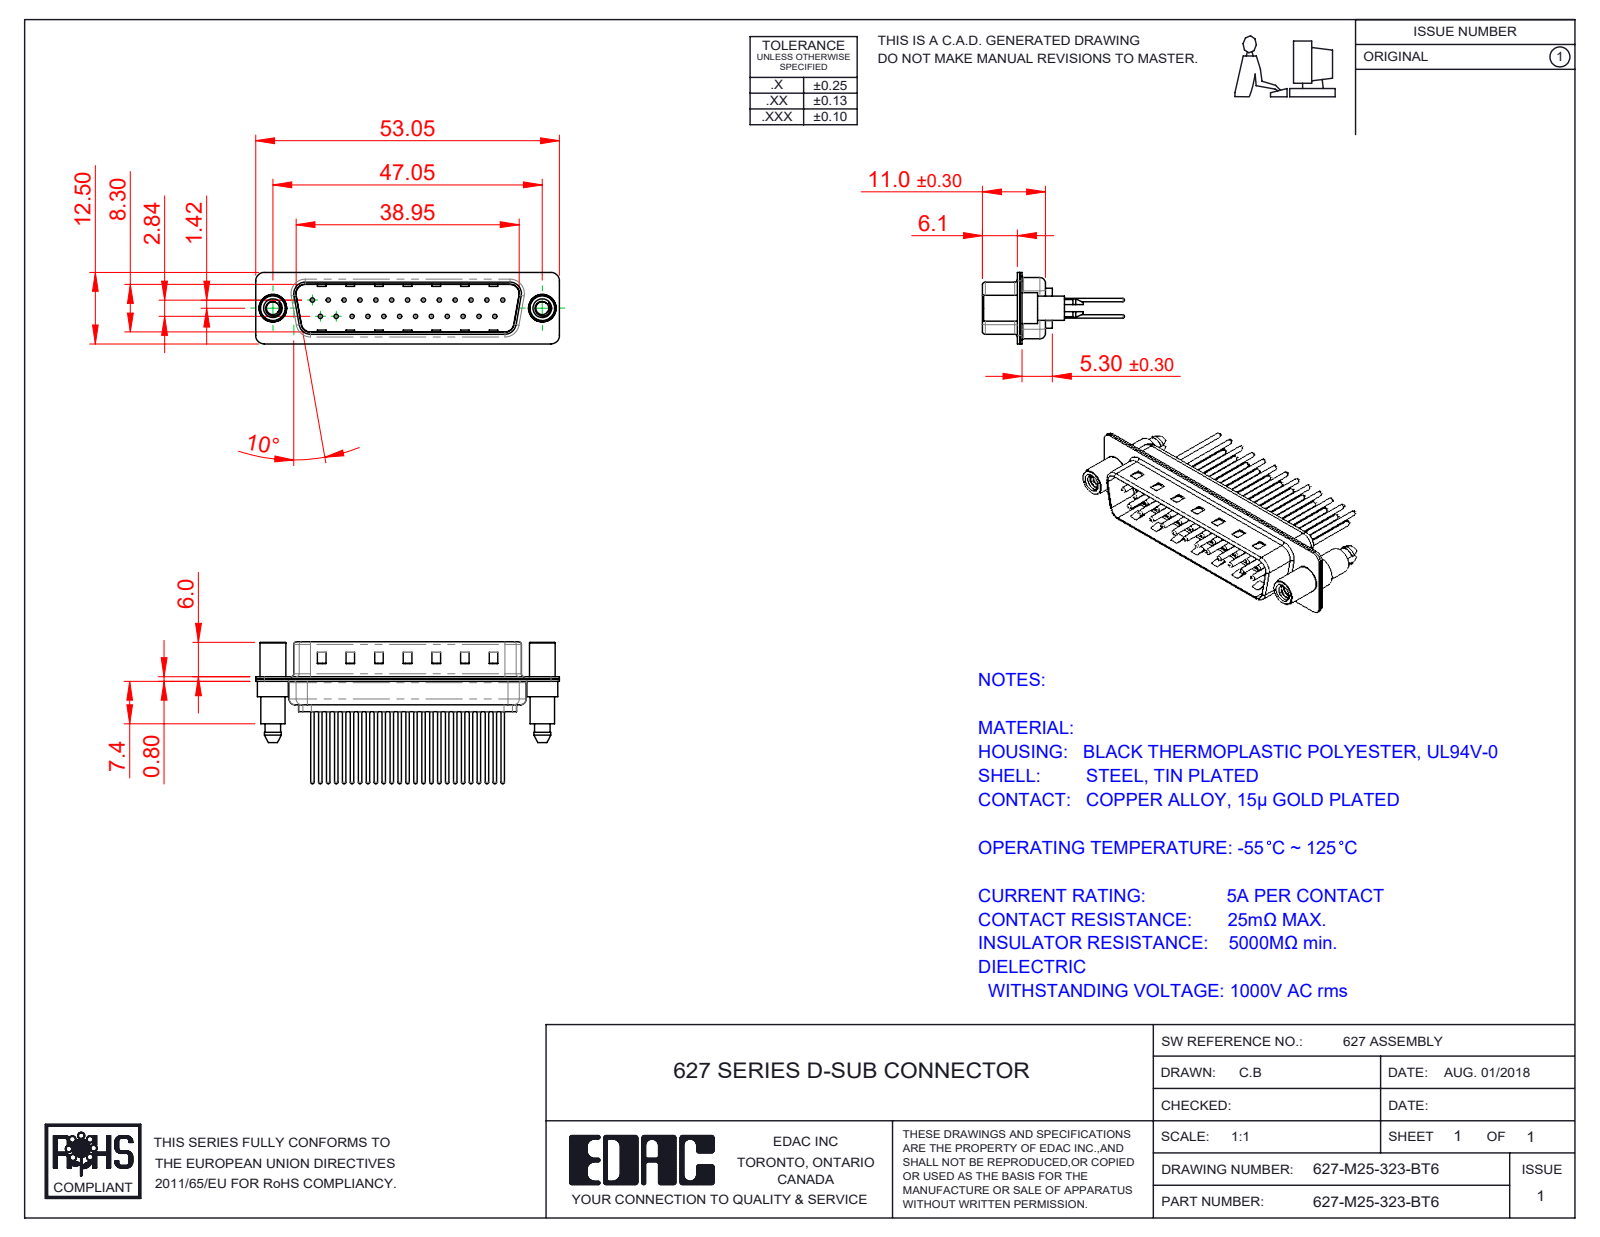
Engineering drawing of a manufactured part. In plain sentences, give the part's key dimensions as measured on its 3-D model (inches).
The part is named "627-M25-323-BT6; 627M Contact Row 2_23; 627M Housing_25 Contacts; 627M Shell Rear_25 Contacts (+3 more)". Its 3-D file was written by "SolidWorks 2020 (CONFIG_CONTROL_DESIGN)". It is 30 solids with 1353 faces: 364 planar, 515 cylindrical and 474 other. Overall it measures 2.089 by 0.975 by 0.492 inches. Its volume is 0.19 cubic inches and its surface area 11.83 square inches. Round holes: 25 of diameter 0.03, 25 of diameter 0.063, 25 of diameter 0.079, 2 of diameter 0.089, 2 of diameter 0.157, 2 of diameter 0.189. Round bosses or shafts: 25 of diameter 0.059, 25 of diameter 0.024, 2 of diameter 0.213, 2 of diameter 0.193, 2 of diameter 0.177, 2 of diameter 0.167. Partial cylindrical surfaces (rounded edges, fillets, slot ends): 18 of radius 0.059, 12 of radius 0.079, 10 of radius 0.063, 8 of radius 0.02, 4 of radius 0.01, 4 of radius 0.024, 4 of radius 0.026, 4 of radius 0.035. The main face-to-face distances are 0.016, 0.031, 0.374, 0.358, 0.343, 0.39, 0.047, 0.224, 0.24, 0.03. The hole center spacings are 0.124, 0.109, 0.218, 0.327, 0.436, 0.545, 0.654, 0.198.
